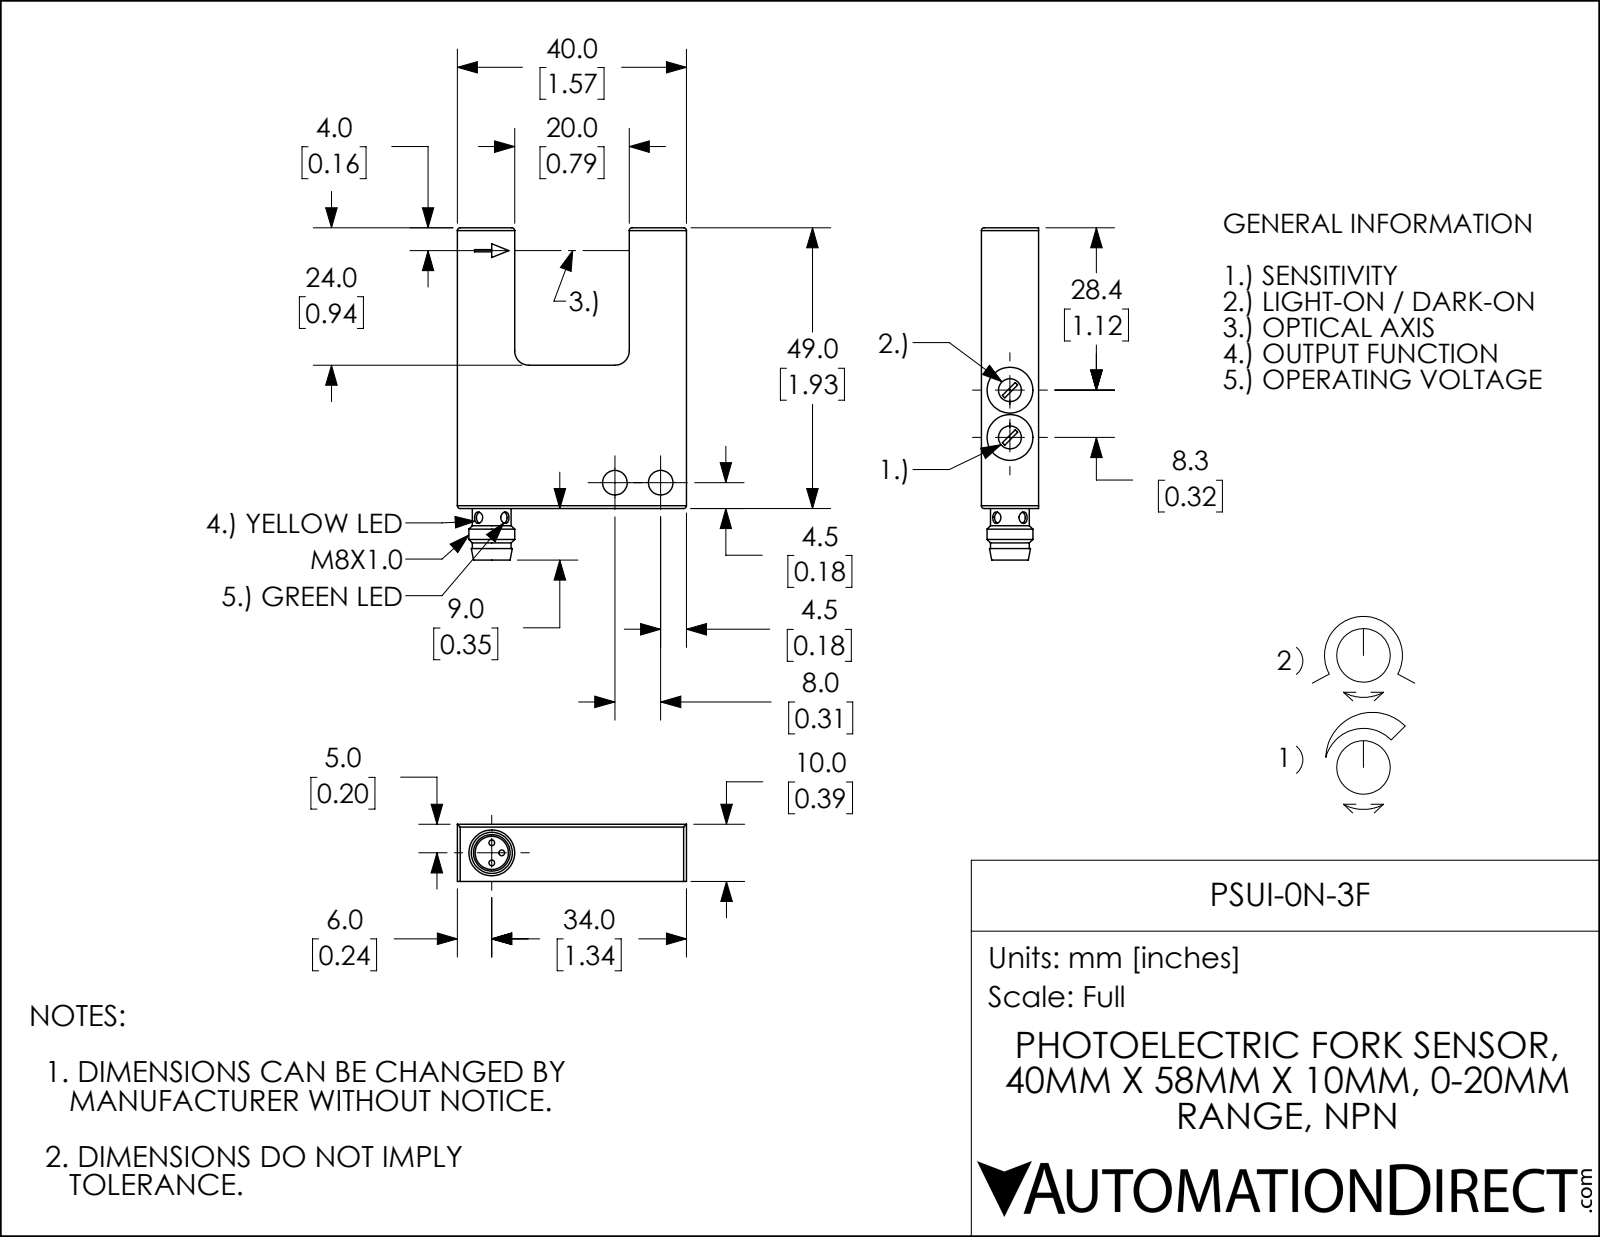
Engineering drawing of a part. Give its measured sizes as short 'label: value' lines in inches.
name: PSUI-0N-3F
written by: SolidWorks 2017 (AUTOMOTIVE_DESIGN)
unit: in
bodies: 1 solid, 73 faces (35 planar, 32 cylindrical, 6 other)
size: 2.283 × 1.575 × 0.394
volume: 0.9 in³; area: 8.934 in²
holes: 2× ⌀0.079, 2× ⌀0.157, 2× ⌀0.169, 2× ⌀0.315, 1× ⌀0.228
bosses: 3× ⌀0.039, 1× ⌀0.315, 1× ⌀0.267
rounds: 8× R0.02, 2× R0.063, 2× R0.098
face distances: 0.394, 1.181, 1.575, 0.787, 1.929, 0.945, 0.984, 0.39, 1.571, 1.177
hole spacings: 0.315, 0.325
